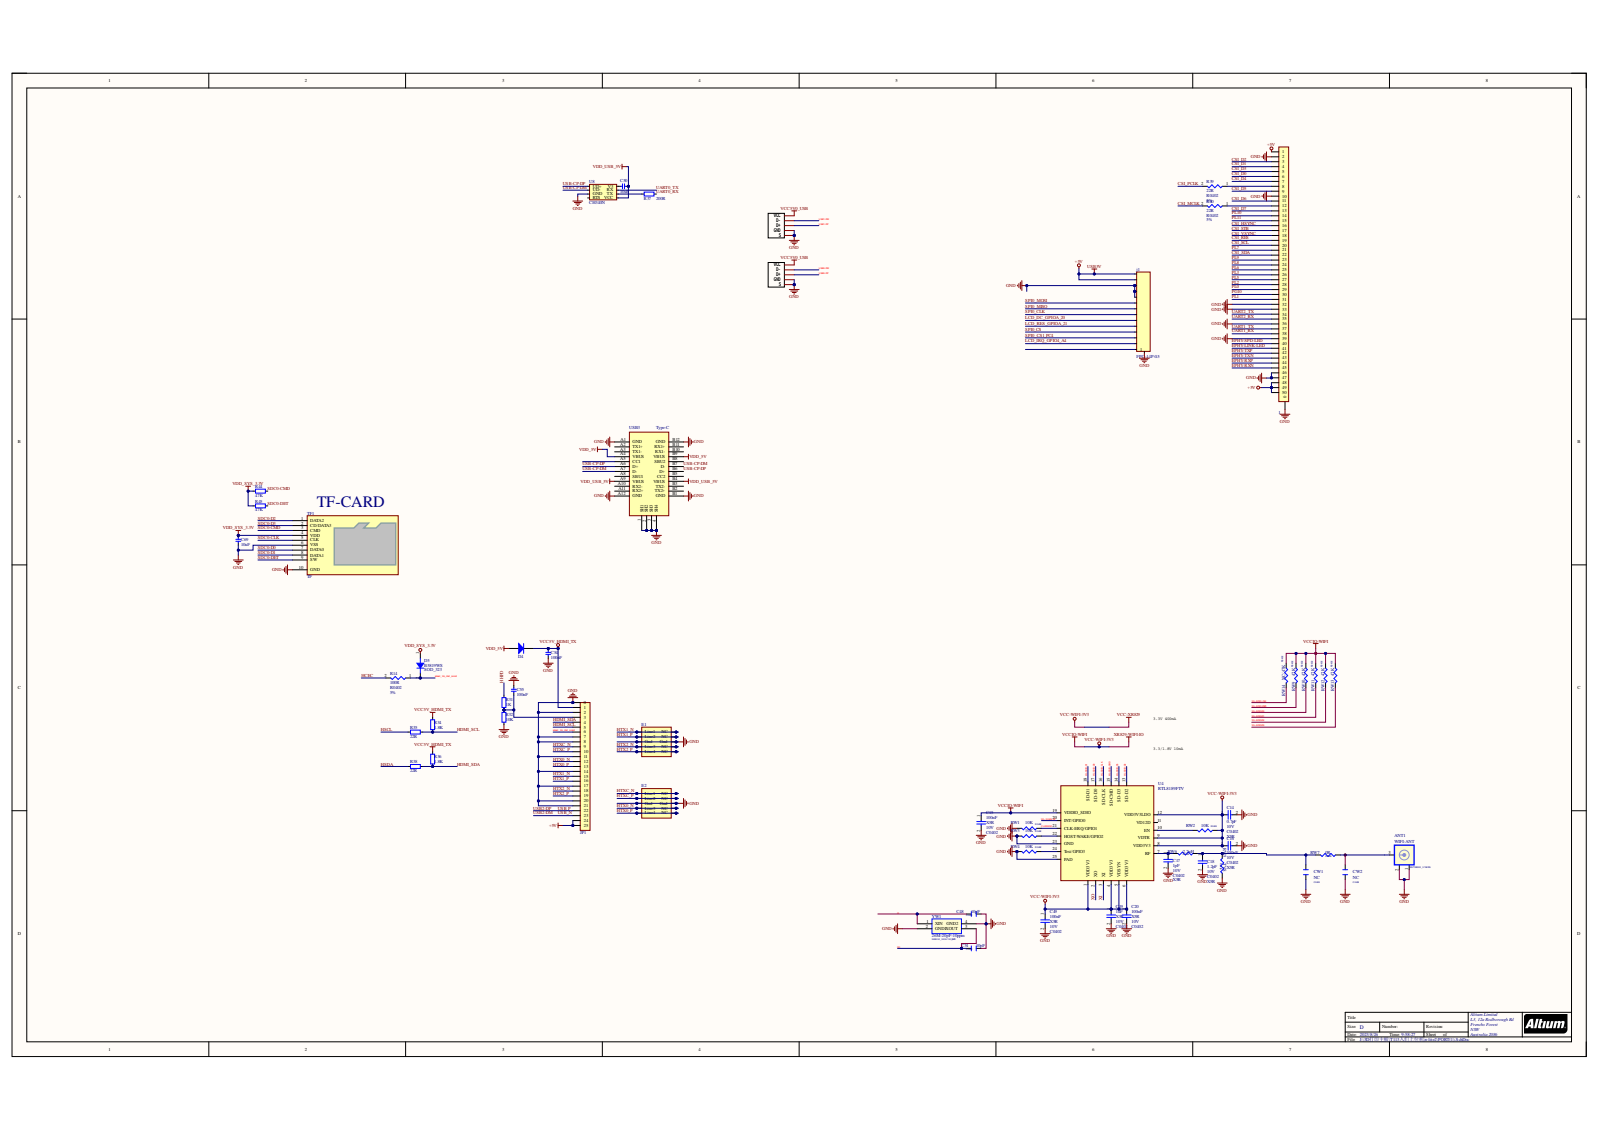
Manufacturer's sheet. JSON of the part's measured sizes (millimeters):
{"part_name": "PCB; Board; C67; 0402_C (+7 more)", "step_written_by": "Open CASCADE 6.8 (AUTOMOTIVE_DESIGN)", "units": "millimeters", "bodies": {"solids": 935, "faces": 20106, "planar": 12877, "cylindrical": 3147, "other": 4082}, "overall_size": [66.49, 37.93, 8.7], "volume_mm3": 3651, "surface_area_mm2": 14936, "round_holes": [[0.65, 9], [0.39, 6], [0.25, 4], [3.2, 4], [0.3, 3], [1.3, 1], [1.8, 1]], "round_bosses_or_shafts": [[0.75, 7], [0.5, 7], [0.45, 6], [1.8, 4], [1.9, 3], [0.2, 3], [2, 1], [1.5, 1]], "partial_cylinders_radius": [[0.1, 103], [0.26, 78], [0.12, 60], [0.2, 56], [0.3, 50], [0.15, 20], [0.35, 12], [0.6, 12]], "face_to_face_distances": [1.01, 1.12, 2, 0.64, 3.01, 5.42, 1.16, 1.25, 1.89, 7.01], "hole_center_spacings": [12.23, 12.39, 14.75, 17.36, 18.38, 18.54, 19.22, 26.34]}
